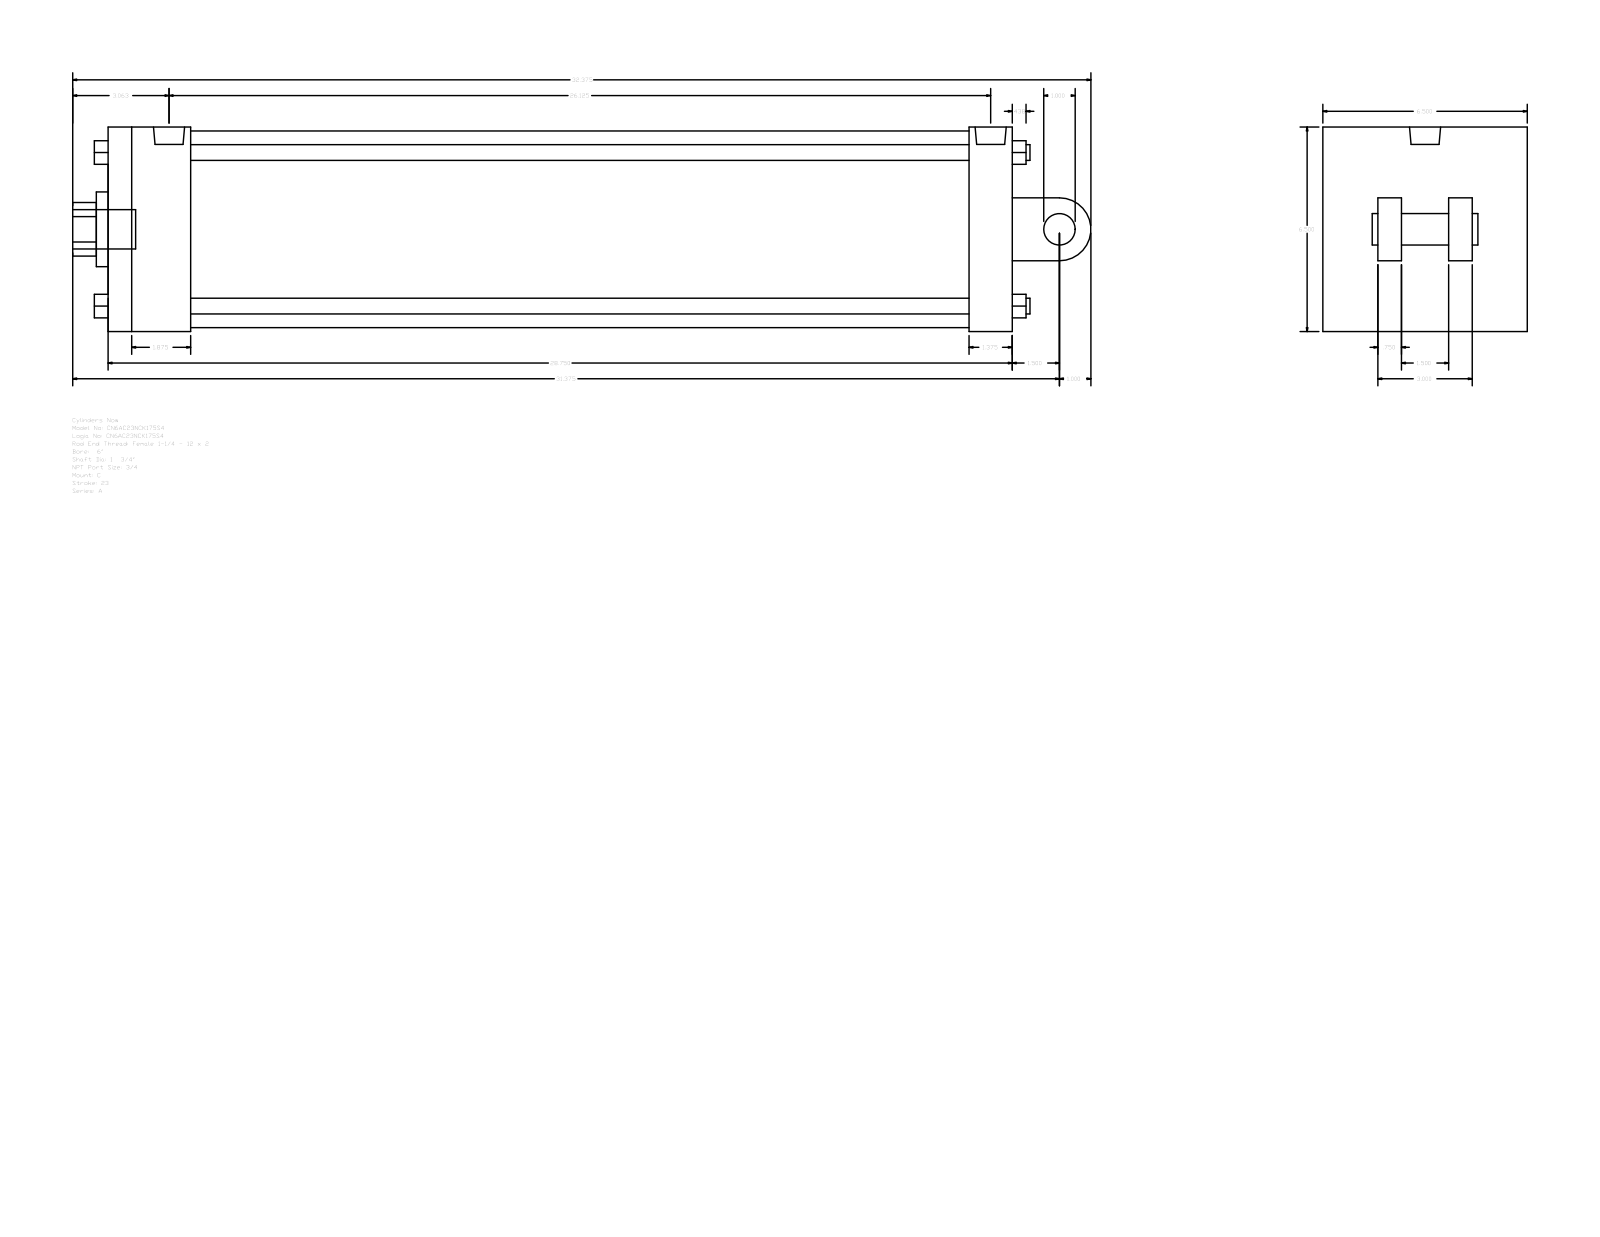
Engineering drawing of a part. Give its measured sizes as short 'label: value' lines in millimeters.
name: A_C__0600_1.75
written by: GSSL Pune (CONFIG_CONTROL_DESIGN)
unit: mm
bodies: 0 solids, 135 faces (102 planar, 33 cylindrical, 0 other)
size: 822.33 × 165.1 × 165.1
holes: 2× ⌀15.08, 1× ⌀25.12, 1× ⌀44.45, 1× ⌀60.33, 1× ⌀158.75
bosses: 4× ⌀12.7, 2× ⌀15.08, 1× ⌀31.75, 1× ⌀25.4, 1× ⌀25.12
rounds: 1× R21.63, 1× R25.4
face distances: 165.1, 730.26, 19.05, 57.15, 66.68, 663.58, 695.33, 628.65, 34.93, 44.45
hole spacings: 5.56
